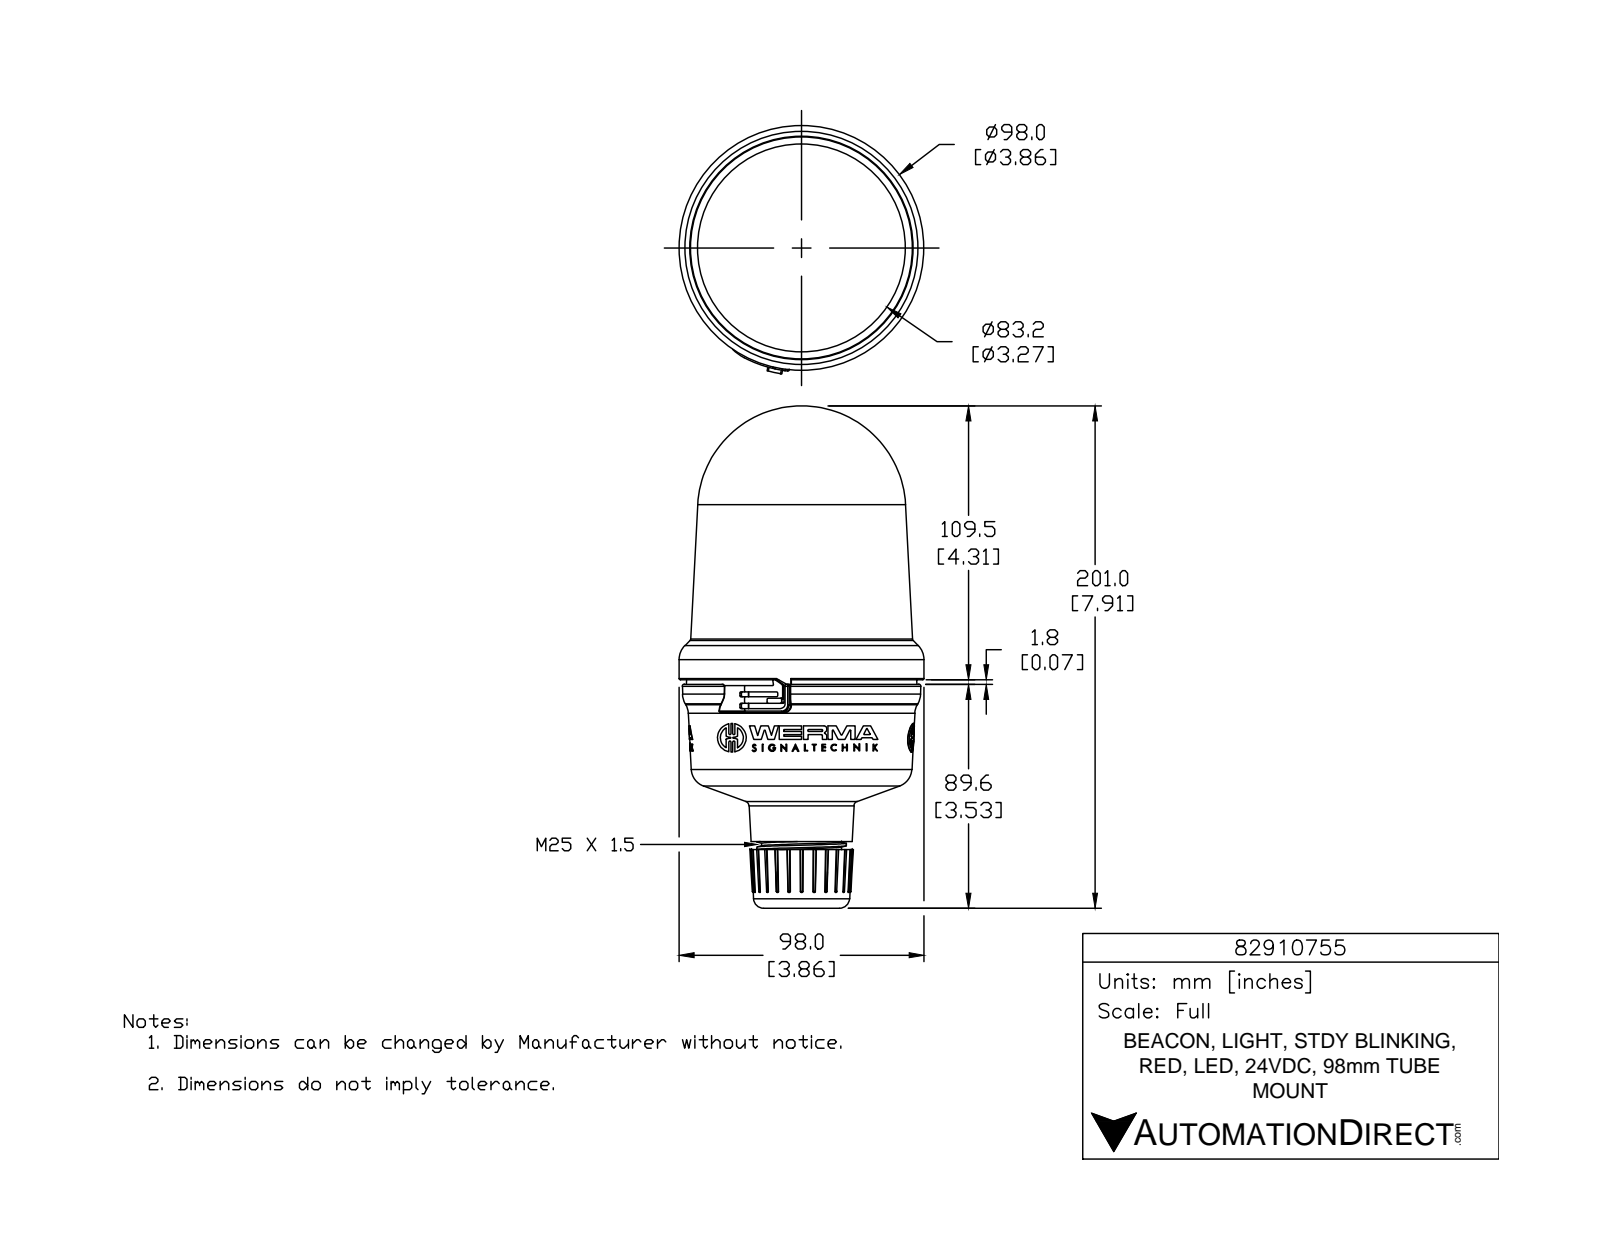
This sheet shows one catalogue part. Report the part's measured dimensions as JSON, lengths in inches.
{"part_name": "82910755", "step_written_by": "SolidWorks 2015 (AUTOMOTIVE_DESIGN)", "units": "inches", "bodies": {"solids": 1, "faces": 1006, "planar": 554, "cylindrical": 189, "other": 263}, "overall_size": [7.914, 3.912, 3.858], "volume_in3": 54.7, "surface_area_in2": 91.39, "round_holes": [[0.078, 3], [1.013, 1], [1.024, 1]], "round_bosses_or_shafts": [[0.452, 3], [0.113, 3], [3.858, 1], [1.409, 1], [1.261, 1]], "partial_cylinders_radius": [[0.02, 12], [0.007, 9], [0.007, 6], [0.016, 6], [0.016, 6], [0.016, 6], [0.262, 6], [0.006, 3]], "face_to_face_distances": [2.214, 0.462, 2.676, 0.335, 0.127, 2.548, 2.603, 2.476, 2.141, 0.073]}
